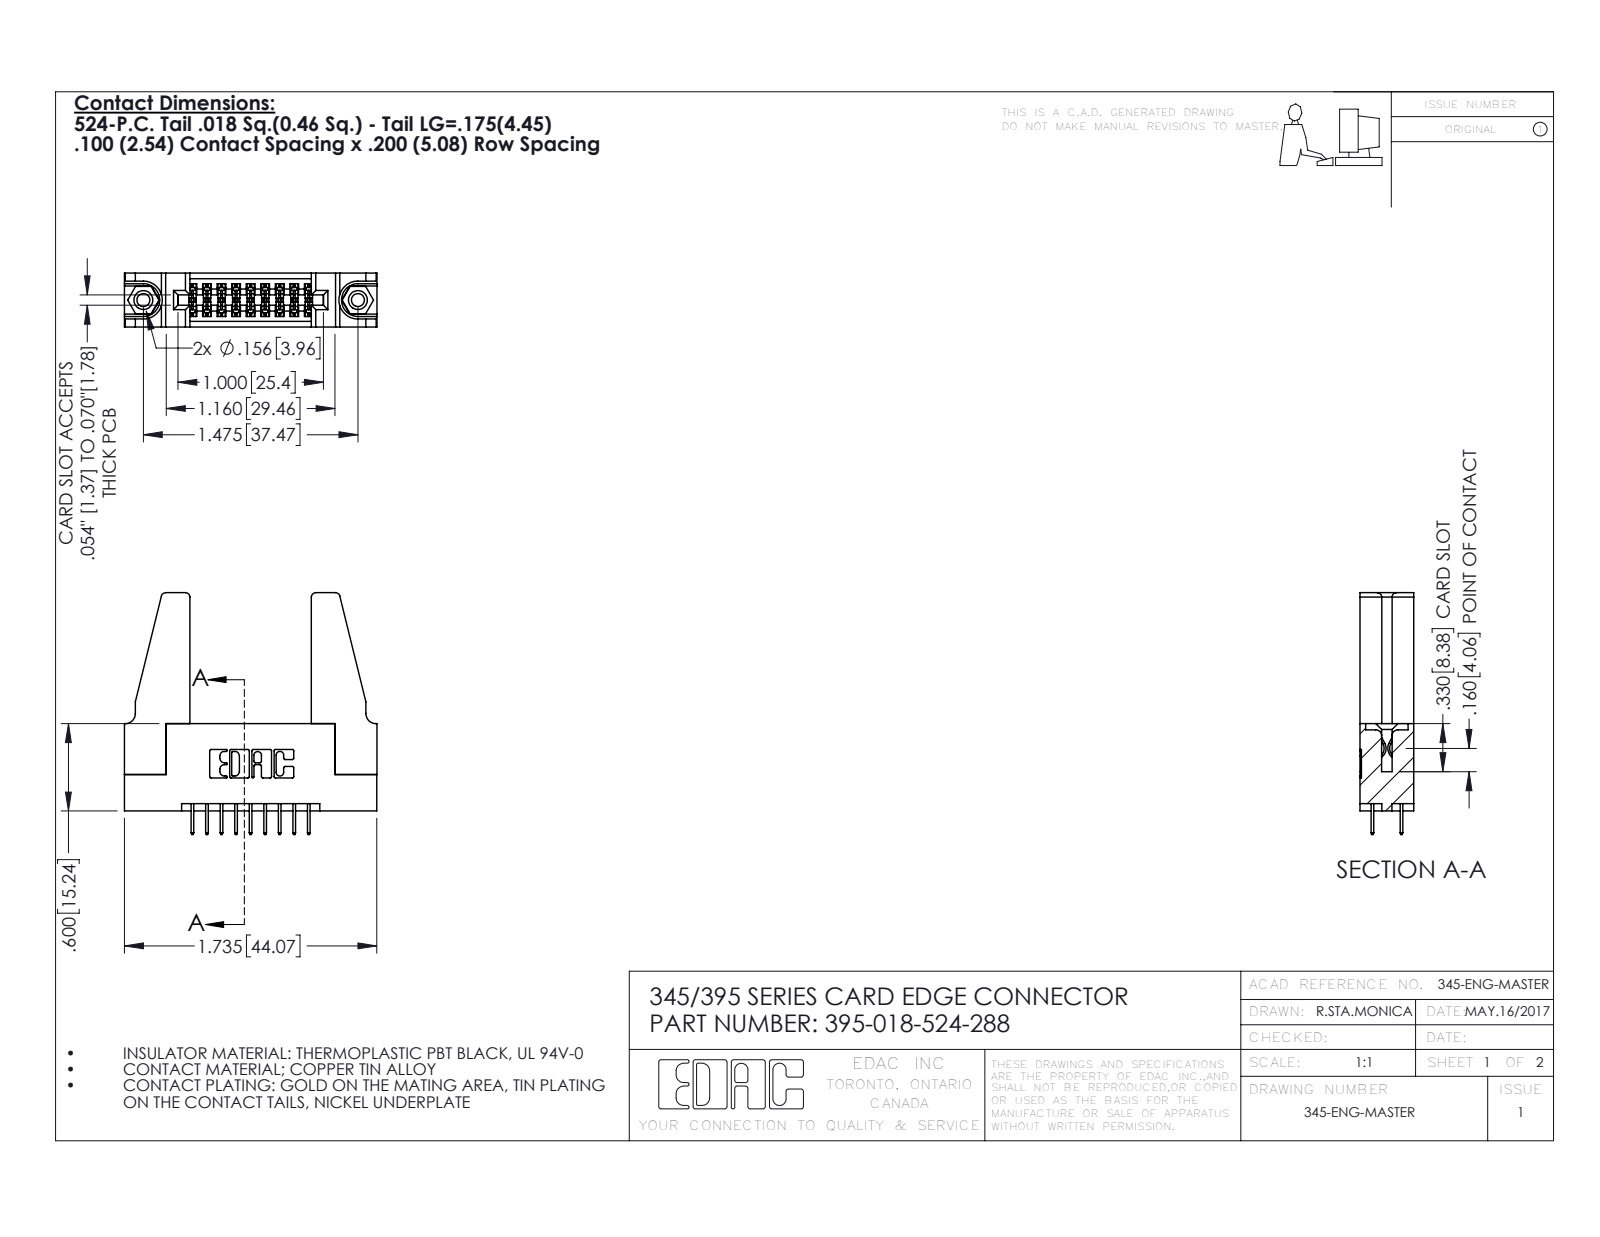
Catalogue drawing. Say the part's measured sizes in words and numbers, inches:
The part is named "345-250-001_345-250-001-102; 345-292-001_345-293-124; 345 Part_Flush Mounting Lugs - 0.156 Dia-TH; 395-018-524-288 (+1 more)". Its 3-D file was written by "SolidWorks 2016 (CONFIG_CONTROL_DESIGN)". It is 23 solids with 1222 faces: 854 planar, 352 cylindrical and 16 other. Overall it measures 1.736 by 1.662 by 0.37 inches. Its volume is 0.44 cubic inches and its surface area 12.79 square inches. Round holes: 2 of diameter 0.089, 2 of diameter 0.125, 2 of diameter 0.156, 1 of diameter 0.064. Round bosses or shafts: 2 of diameter 0.155. Partial cylindrical surfaces (rounded edges, fillets, slot ends): 27 of radius 0.006, 22 of radius 0.01, 8 of radius 0.03, 6 of radius 0.007, 6 of radius 0.031, 3 of radius 0.026, 2 of radius 0.014, 2 of radius 0.019. The main face-to-face distances are 0.37, 0.072, 0.298, 0.2, 0.225, 0.098, 0.272, 0.025, 0.15, 0.148. The hole center spacings are 0.27, 1.244, 1.475.
